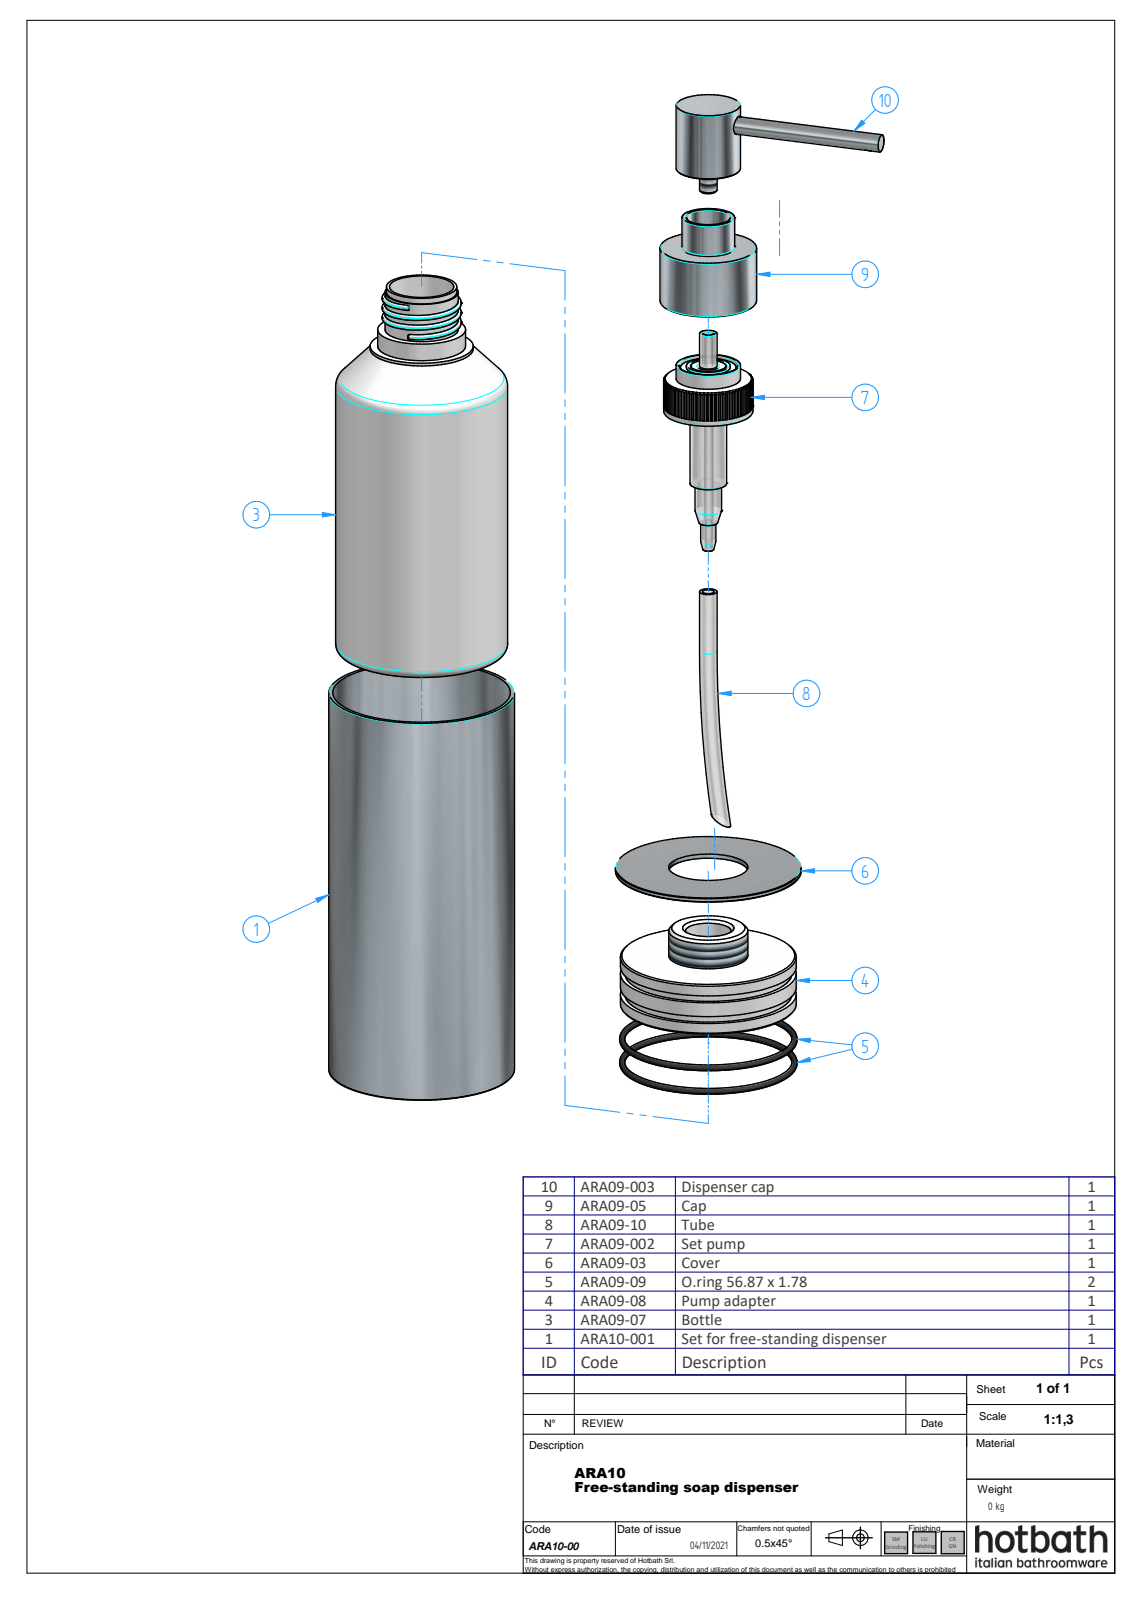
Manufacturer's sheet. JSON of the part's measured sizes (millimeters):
{"part_name": "ARA10-00; ARA10-001; ARA10-01; ARA09-02 (+5 more)", "step_written_by": "ST-DEVELOPER v16.7 (AP242_MANAGED_MODEL_BASED_3D_ENGINEERING_MIM_LF)", "units": "millimeters", "bodies": {"solids": 6, "faces": 68, "planar": 19, "cylindrical": 23, "other": 26}, "overall_size": [189, 94.7, 63.4], "volume_mm3": 55325, "surface_area_mm2": 75849, "round_holes": [[3.5, 2], [2.5, 1], [4.13, 1], [6.2, 1], [15, 1], [18.5, 1], [27, 1], [30, 1], [30.7, 1], [31, 1], [60.6, 1]], "round_bosses_or_shafts": [[6, 2], [63.4, 1], [60.5, 1], [33, 1], [22, 1], [18, 1], [8, 1], [5, 1]], "face_to_face_distances": [1.5, 136.5, 138, 135, 157.5, 156, 21, 19.5, 155.5, 154], "hole_center_spacings": [58.5]}
